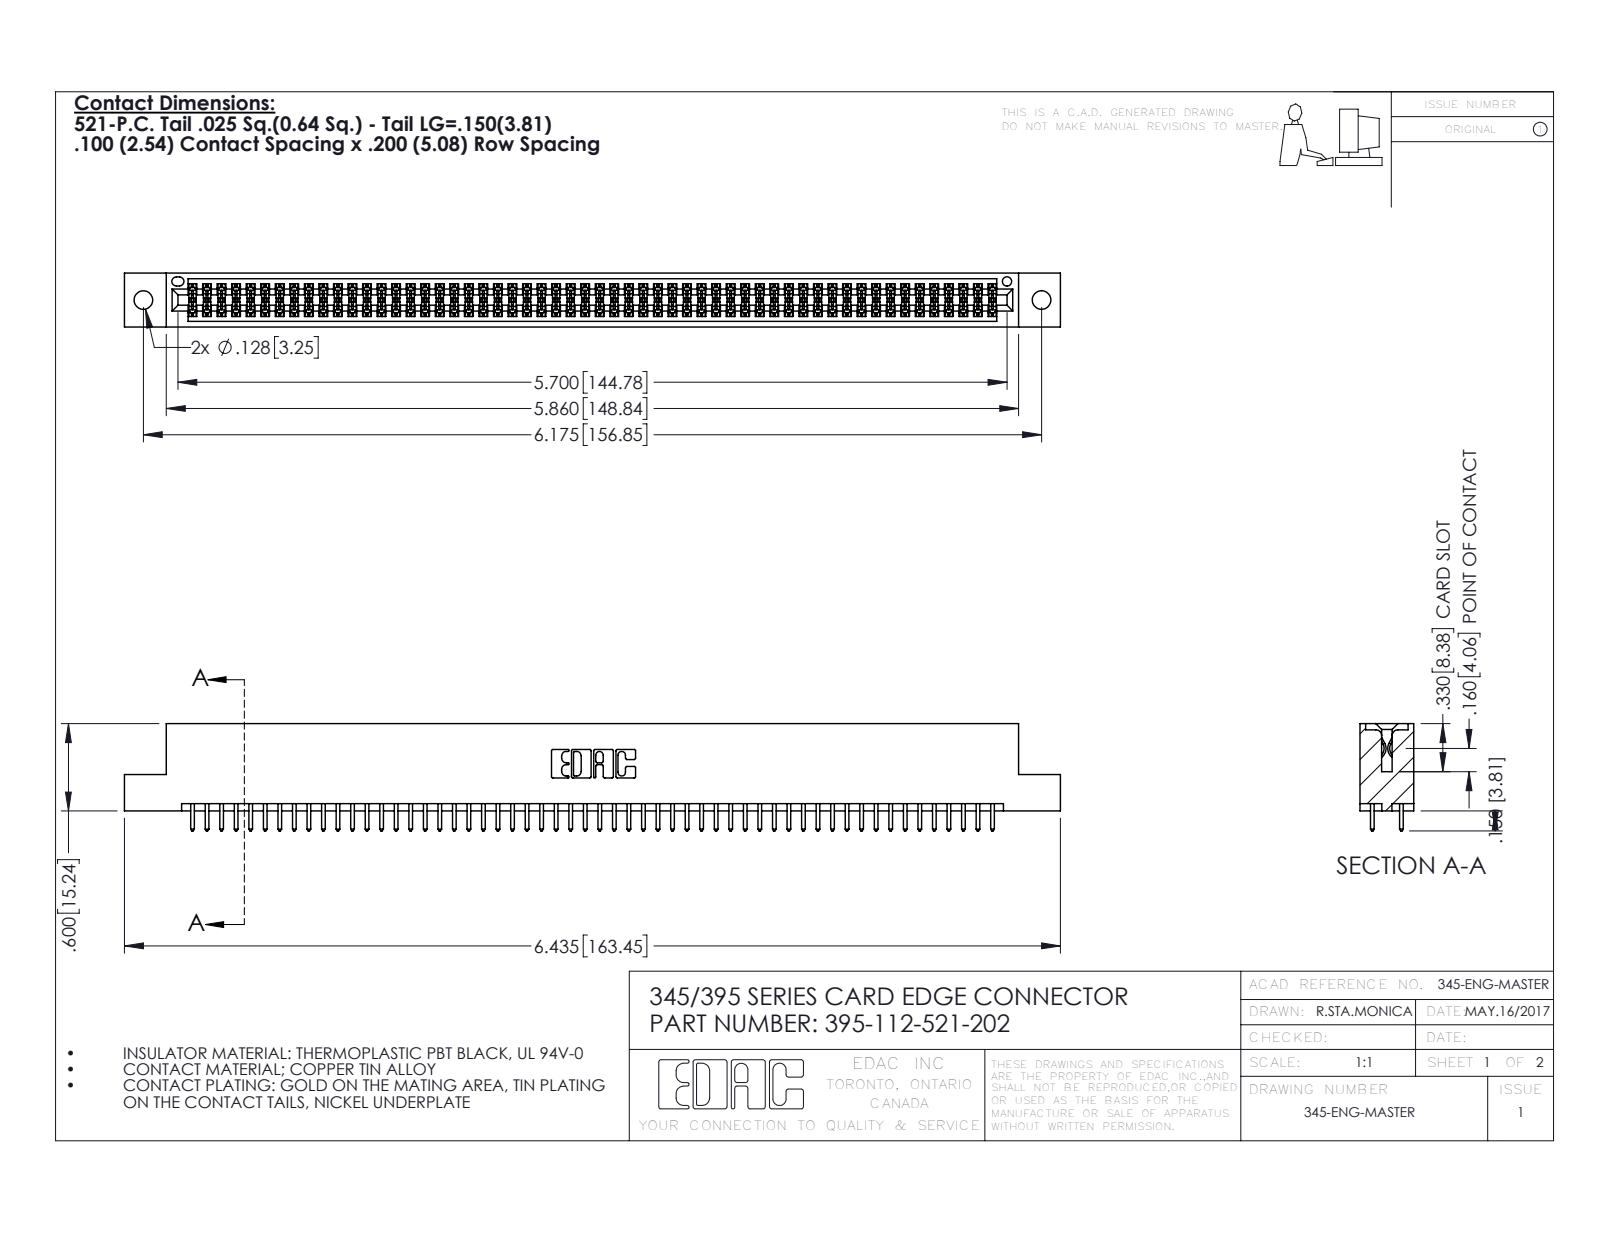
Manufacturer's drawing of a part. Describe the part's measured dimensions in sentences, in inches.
The part is named "345 Part_Flush Mounting Lugs - 0.128 Dia; 395-112-521-202; 345-292-001_345-293-121". Its 3-D file was written by "SolidWorks 2016 (CONFIG_CONTROL_DESIGN)". It is 113 solids with 5726 faces: 3776 planar, 1950 cylindrical and 0 other. Overall it measures 6.435 by 0.737 by 0.37 inches. Its volume is 0.972 cubic inches and its surface area 36.02 square inches. Round holes: 2 of diameter 0.128, 1 of diameter 0.064. Partial cylindrical surfaces (rounded edges, fillets, slot ends): 168 of radius 0.006, 112 of radius 0.01, 22 of radius 0.01, 6 of radius 0.007, 6 of radius 0.031, 3 of radius 0.026, 2 of radius 0.014, 2 of radius 0.019. The main face-to-face distances are 0.298, 0.072, 0.2, 0.098, 0.272, 0.025, 0.37, 0.225, 0.175, 0.149. The hole center spacings are 0.27, 5.939, 6.175.
